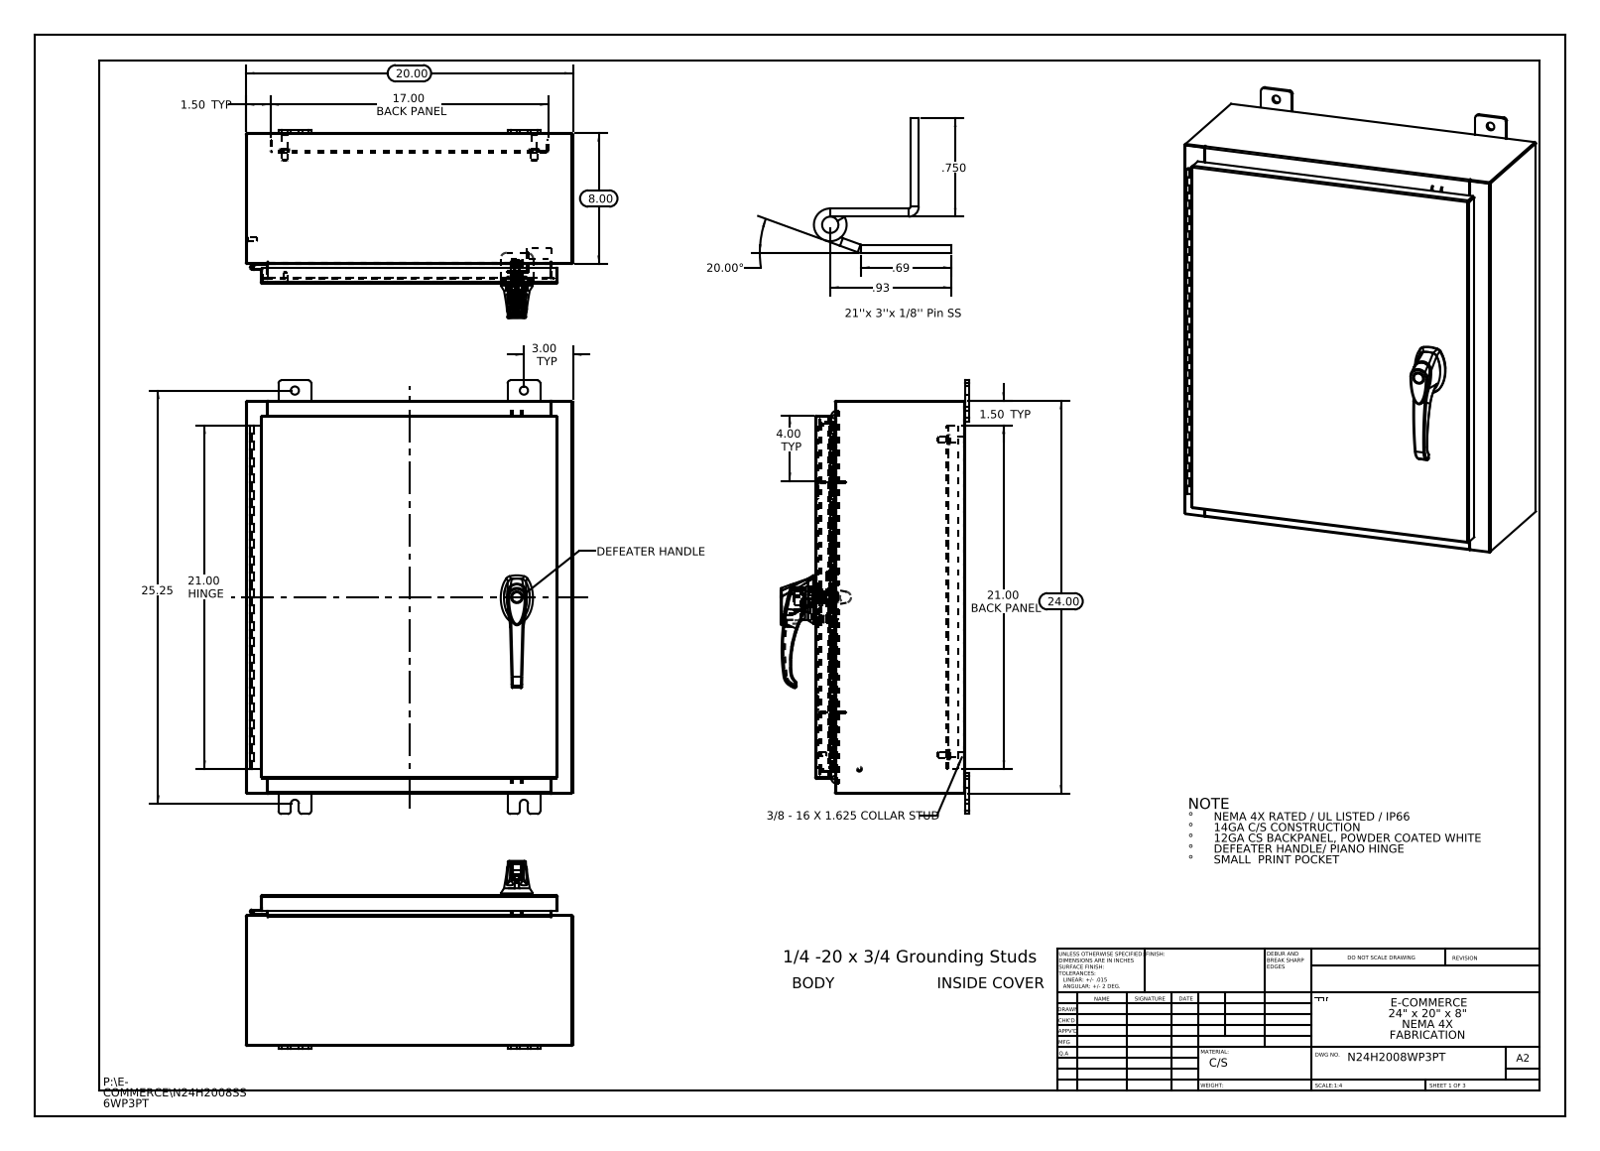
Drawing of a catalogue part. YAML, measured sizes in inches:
part_name: "N24H2008SS6WP3PT Bottom; 012103_012102; N24H2008SS6WP3PT Backpanel; g26103103_26163303 (+8 more)"
step_written_by: "SolidWorks 2013 (CONFIG_CONTROL_DESIGN)"
units: inches
bodies: {solids: 37, faces: 2498, planar: 883, cylindrical: 917, other: 698}
overall_size: [26.5, 20, 11.495]
volume: 194.3
surface_area: 4805
round_holes:
  - {diameter: 0.5, count: 8}
  - {diameter: 0.25, count: 4}
  - {diameter: 0.138, count: 3}
  - {diameter: 0.161, count: 3}
  - {diameter: 0.079, count: 2}
  - {diameter: 0.203, count: 2}
  - {diameter: 0.313, count: 2}
  - {diameter: 0.437, count: 2}
  - {diameter: 0.125, count: 1}
  - {diameter: 0.125, count: 1}
  - {diameter: 0.197, count: 1}
  - {diameter: 0.276, count: 1}
round_bosses_or_shafts:
  - {diameter: 0.625, count: 4}
  - {diameter: 0.375, count: 4}
  - {diameter: 0.33, count: 4}
  - {diameter: 0.157, count: 4}
  - {diameter: 0.14, count: 4}
  - {diameter: 0.315, count: 3}
  - {diameter: 0.236, count: 3}
  - {diameter: 1.181, count: 1}
partial_cylinders:
  - {radius: 0.118, count: 37}
  - {radius: 0.006, count: 33}
  - {radius: 0.19, count: 24}
  - {radius: 0.013, count: 22}
  - {radius: 0.088, count: 18}
  - {radius: 0.039, count: 15}
  - {radius: 0.028, count: 12}
  - {radius: 0.008, count: 6}
face_to_face_distances: [0.075, 9.126, 9.051, 9.201, 0.104, 19.925, 1, 1.075, 8.051, 8.126]
hole_center_spacings: [7.68, 0.295, 0.625, 0.841, 1.25, 1.313, 1.561, 1.858]
